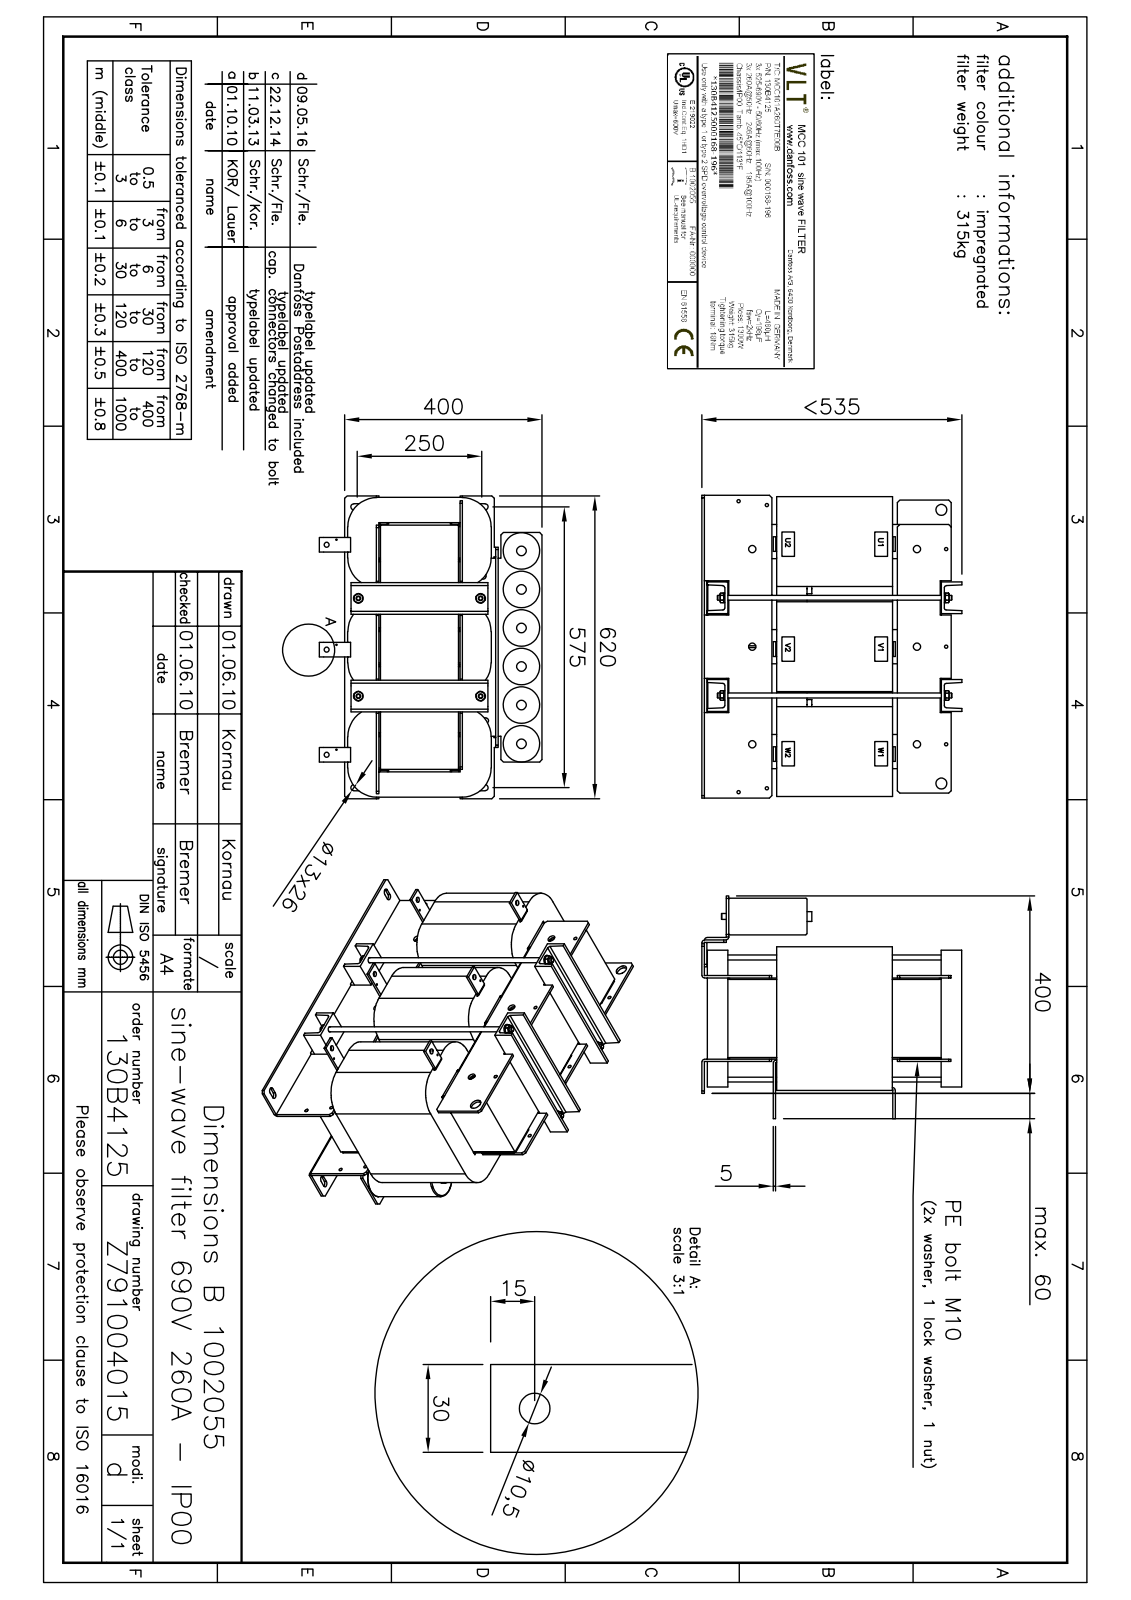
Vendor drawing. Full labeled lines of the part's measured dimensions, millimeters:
Part name (STEP PRODUCT): Baugruppe B 1002055; +3810-0090; #050-0967; #700-1359 (+8 more)
STEP written by: SolidWorks 2012 (AUTOMOTIVE_DESIGN)
Units: millimetres
Bodies: 129 solids, 2467 faces (1212 planar, 769 cylindrical, 486 other)
Overall size (bounding box): 620 × 532 × 451
Volume: 57 270 000 mm³ · Surface area: 4 898 000 mm²
Round holes (diameter × count): ⌀10.5 ×13, ⌀8.5 ×10, ⌀10 ×10, ⌀7.1 ×7, ⌀10.2 ×7, ⌀3.3 ×6, ⌀12 ×6, ⌀13 ×6, ⌀15 ×6, ⌀10.1 ×5, ⌀11 ×4, ⌀4.3 ×3
Round bosses / shafts (diameter × count): ⌀20 ×16, ⌀64 ×6, ⌀17 ×5, ⌀11.3 ×5, ⌀12 ×3, ⌀9 ×3, ⌀8 ×3, ⌀6 ×3
Partial cylindrical surfaces — rounded edges, fillets, slot ends (radius × count): R0.92 ×60, R0.1 ×19, R3.1 ×12, R50 ×12, R4 ×8, R6.5 ×8, R7.5 ×8, R5.1 ×7
Main face-to-face distances: 5, 3, 215, 157, 160, 165, 50, 8, 55, 430
Hole centre spacings: 200, 22.36, 215, 79, 158, 205.97, 208.81, 225.89
